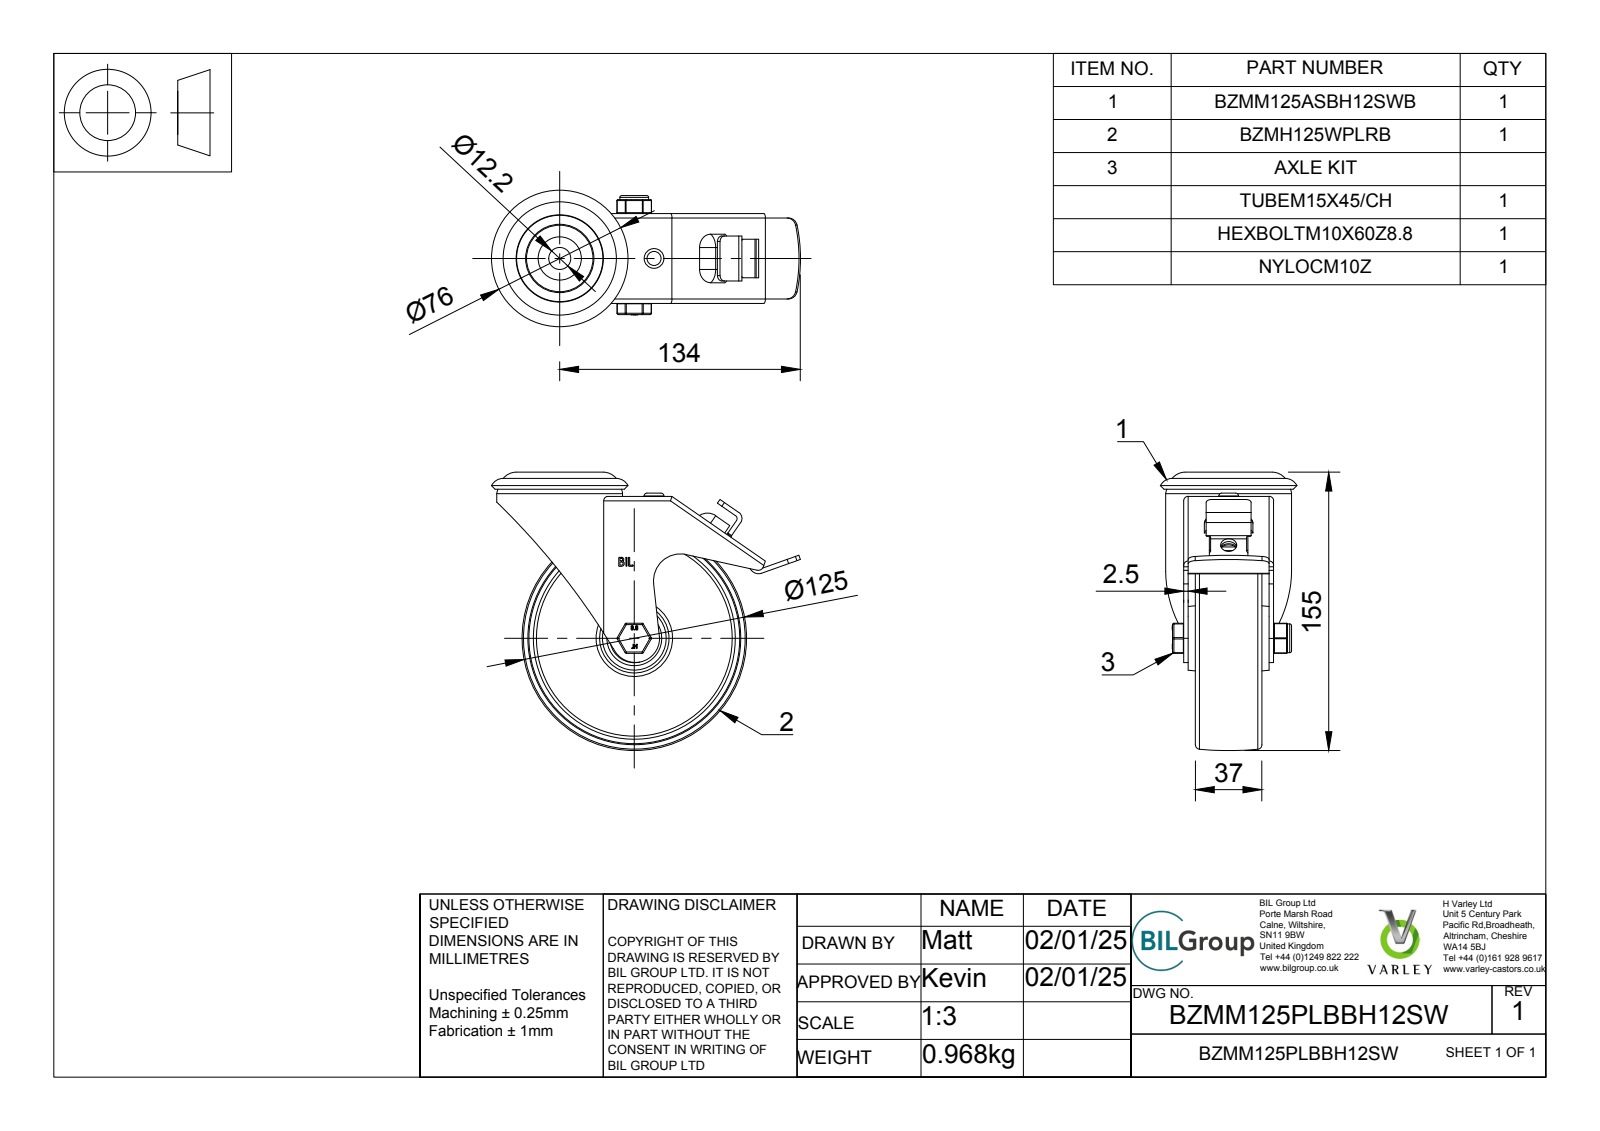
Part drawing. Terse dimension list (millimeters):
name: BZMM125PLBBH12SW v3; BZMM125ASBH12SWB v2; ZINC PLATED, PRESSED STEEL HEAD; ZINC PLATED, PRESSED STEEL FORKS (+8 more)
written by: Autodesk Translation Framework v13.20.0.188 (AP242_MANAGED_MODEL_BASED_3D_ENGINEERING_MIM_LF)
unit: mm
bodies: 20 solids, 723 faces (365 planar, 244 cylindrical, 114 other)
size: 172 × 155 × 76
volume: 288 394 mm³; area: 145 341 mm²
holes: 2× ⌀6, 1× ⌀9, 1× ⌀10, 1× ⌀10.2, 1× ⌀12, 1× ⌀12.2, 1× ⌀15.5, 1× ⌀23, 1× ⌀30.5, 1× ⌀65, 1× ⌀72
bosses: 8× ⌀4, 1× ⌀70, 1× ⌀49.5, 1× ⌀38, 1× ⌀24, 1× ⌀21.31, 1× ⌀16, 1× ⌀14.95
rounds: 60× R0.75, 32× R0.5, 7× R1.5, 6× R1.25, 6× R3, 6× R4, 5× R2.5, 3× R2
face distances: 2.5, 19, 7, 26, 21.5, 28.5, 47.5, 45, 50, 6.5
hole spacings: 52.5
